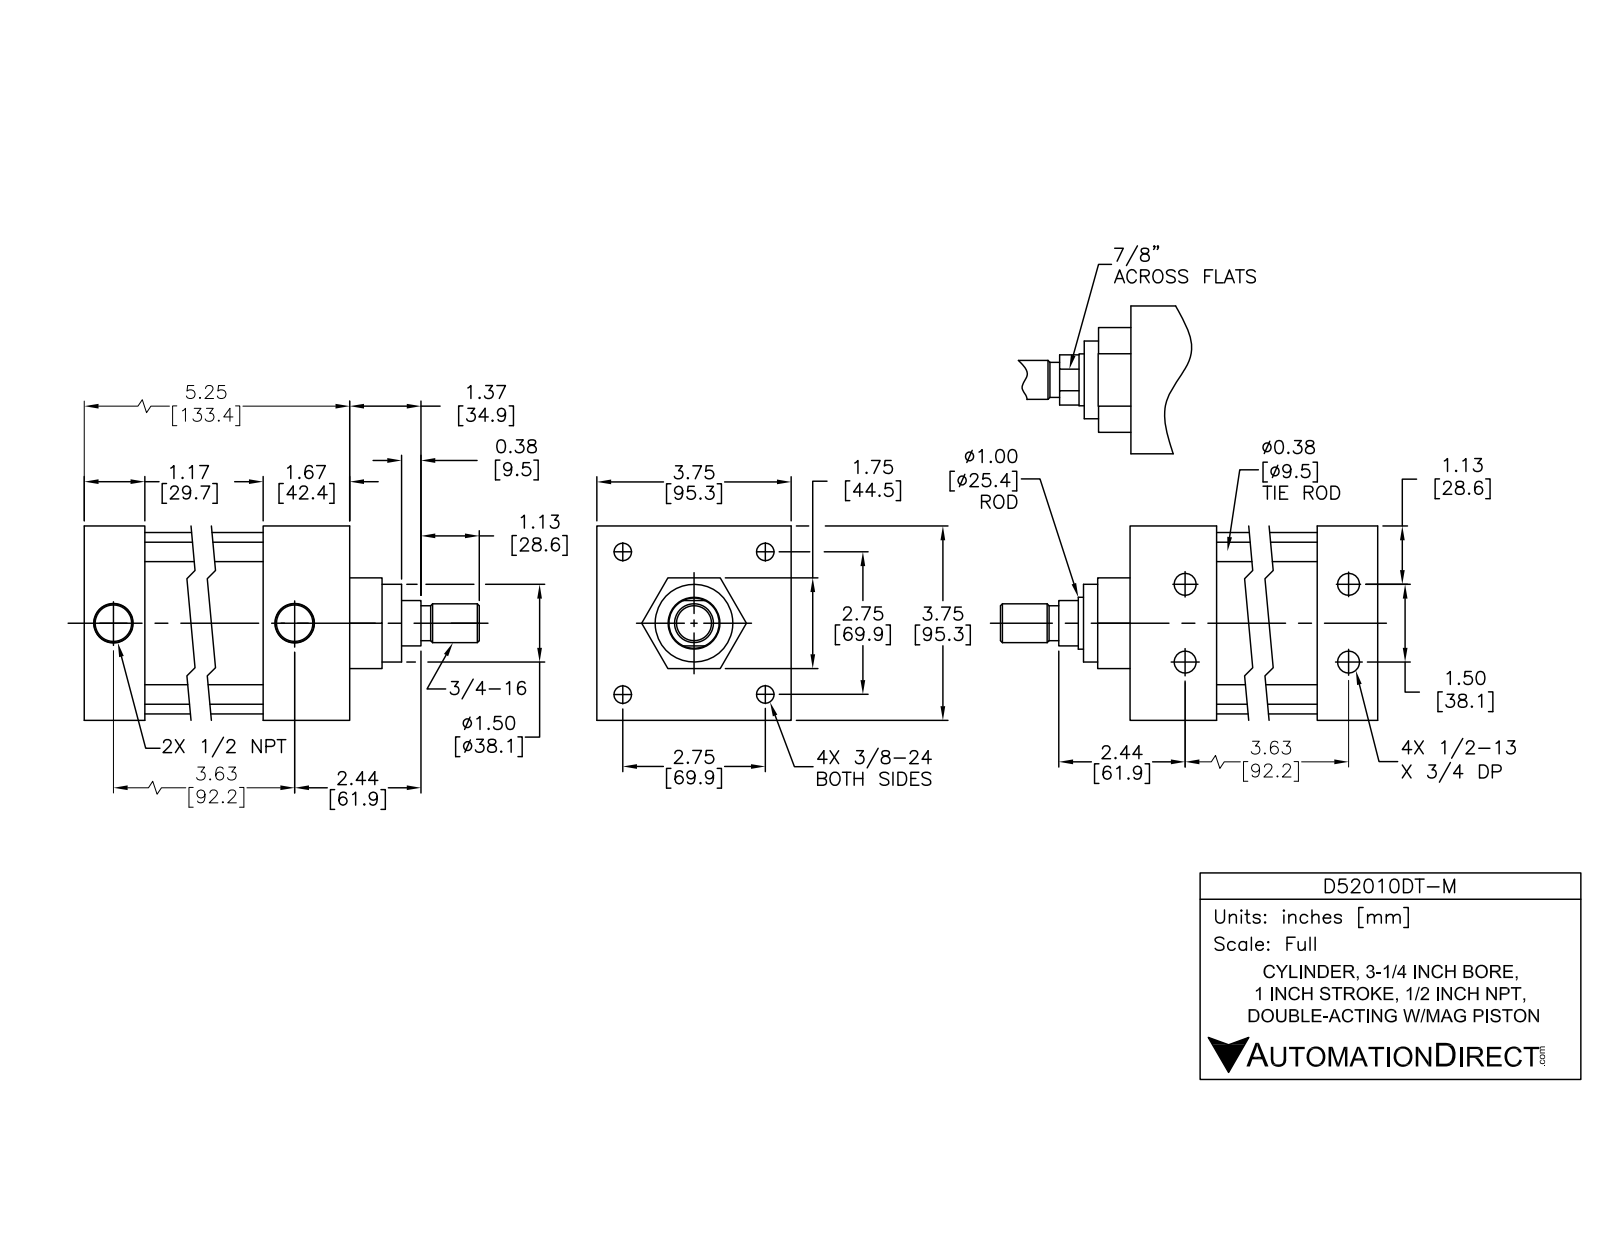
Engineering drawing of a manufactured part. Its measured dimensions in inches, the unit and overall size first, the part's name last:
Units: inches
Overall size (bounding box): 7.745 × 3.75 × 3.75
Round holes (diameter × count): ⌀0.33 ×4, ⌀0.406 ×4, ⌀0.417 ×4, ⌀0.625 ×4, ⌀0.5 ×2, ⌀0.766 ×2, ⌀1 ×1, ⌀1.003 ×1, ⌀3.25 ×1
Round bosses / shafts (diameter × count): ⌀0.609 ×4, ⌀0.375 ×4, ⌀0.34 ×4, ⌀3.5 ×1, ⌀3.247 ×1, ⌀1.75 ×1, ⌀0.997 ×1, ⌀0.97 ×1
Partial cylindrical surfaces — rounded edges, fillets, slot ends (radius × count): R0.375 ×4
Main face-to-face distances: 3.75, 0.08, 2.326, 5.246, 1.75, 3.997, 1.249, 2.751, 1.246, 2.495
Hole centre spacings: 0.75, 0.76, 1.5, 1.95, 1.95, 2.758, 2.758, 3.5
Volume: 56.3 in³ · Surface area: 265.7 in²
Bodies: 12 solids, 303 faces (99 planar, 114 cylindrical, 90 other)
Part name (STEP PRODUCT): D52010DT-M BODY; D52010DT-M PISTON; D52010DT-M
STEP written by: SolidWorks 2015 (AUTOMOTIVE_DESIGN)
